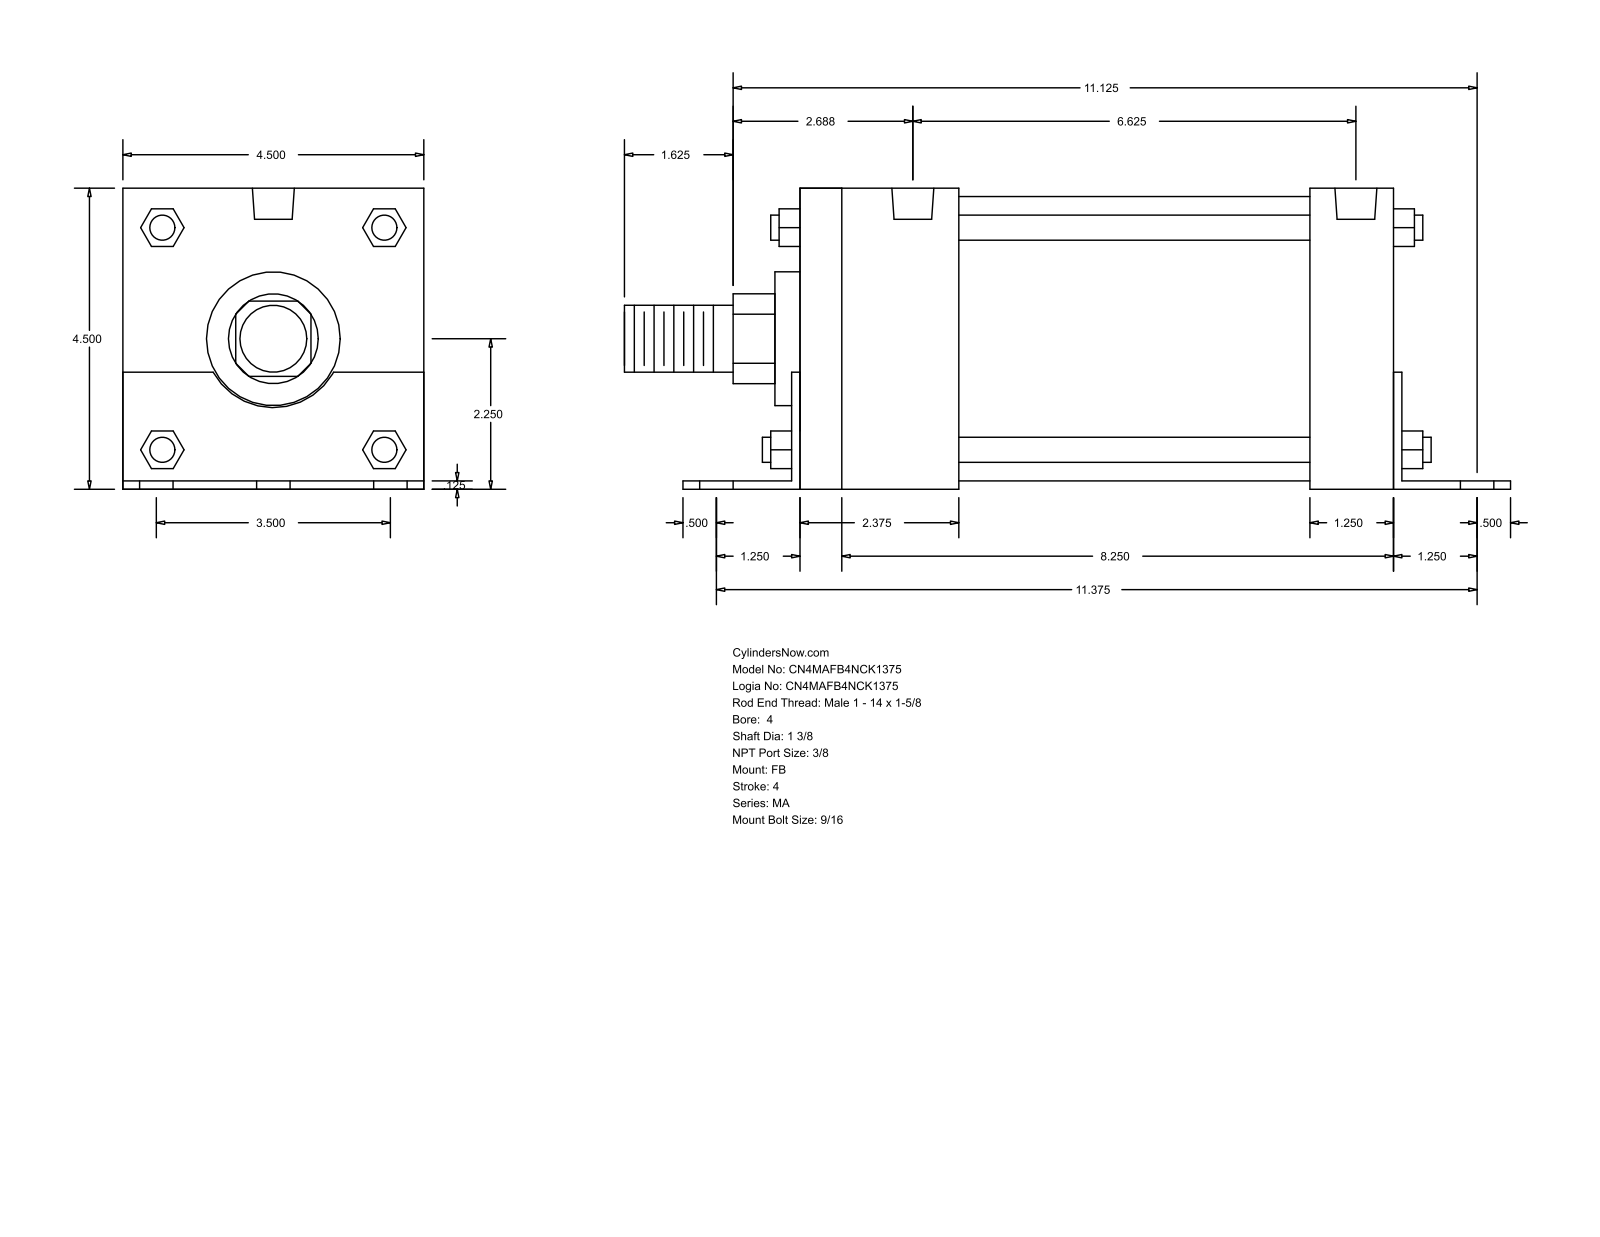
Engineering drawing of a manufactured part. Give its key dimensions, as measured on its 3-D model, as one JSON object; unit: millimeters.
{"part_name": "MA_FB__0400_1.375", "step_written_by": "GSSL Pune (CONFIG_CONTROL_DESIGN)", "units": "millimeters", "bodies": {"solids": 0, "faces": 140, "planar": 105, "cylindrical": 35, "other": 0}, "overall_size": [336.55, 114.35, 114.3], "round_holes": [[14.29, 6], [11.11, 4], [15.93, 2]], "round_bosses_or_shafts": [[9.53, 4], [107.95, 1], [50.8, 1], [34.92, 1], [25.4, 1]], "partial_cylinders_radius": [[17.06, 1], [26.16, 1]], "face_to_face_distances": [114.3, 3.17, 114.35, 3.12, 111.18, 225.42, 3.18, 228.6, 34.93, 228.59], "hole_center_spacings": [44.45, 292.32, 288.92, 63.99, 67.49, 86.85, 88.9, 90.98]}
